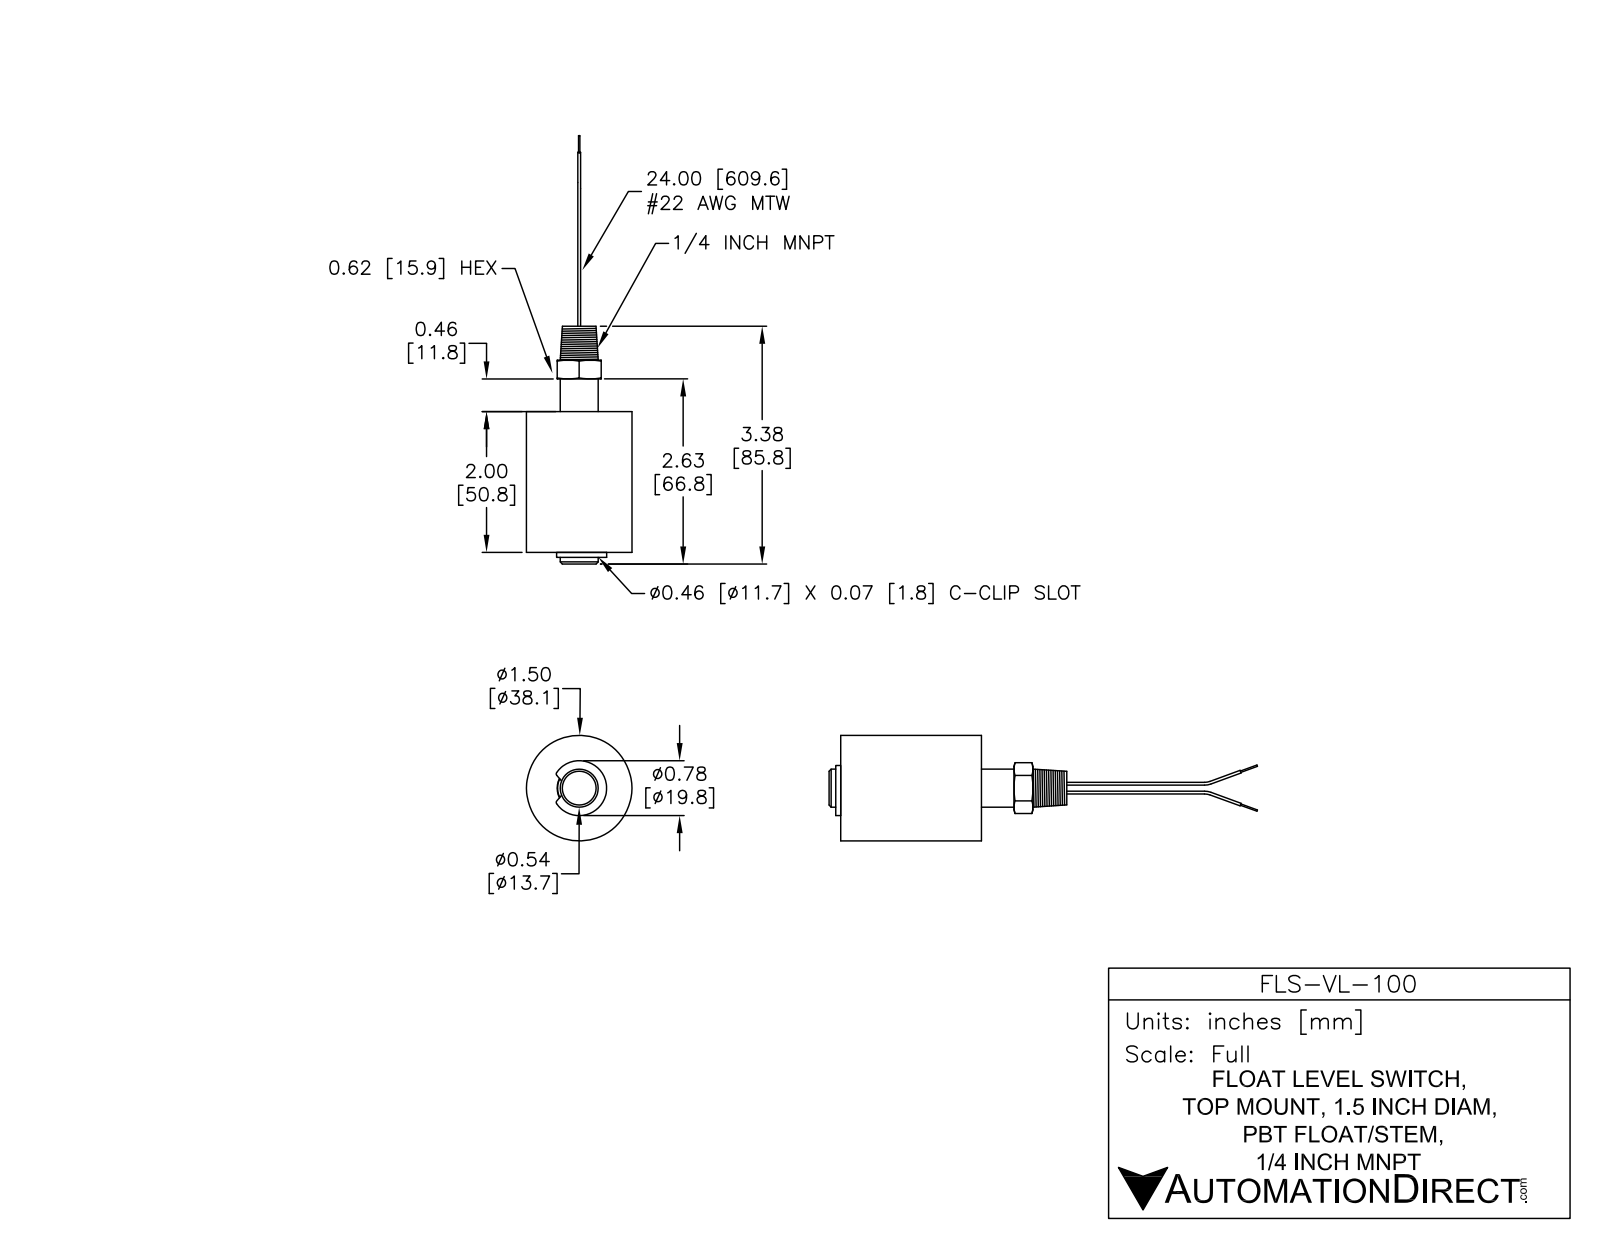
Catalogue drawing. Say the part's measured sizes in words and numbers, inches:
The part is named "FLS-VL-100". Its 3-D file was written by "SolidWorks 2013 (AUTOMOTIVE_DESIGN)". It is 5 solids with 68 faces: 25 planar, 35 cylindrical and 8 other. Overall it measures 6.099 by 1.5 by 1.5 inches. Its volume is 3.173 cubic inches and its surface area 28.35 square inches. Round holes: 1 of diameter 0.45, 1 of diameter 0.46, 1 of diameter 0.63. Round bosses or shafts: 4 of diameter 0.04, 2 of diameter 0.02, 1 of diameter 1.5, 1 of diameter 0.78, 1 of diameter 0.54. Partial cylindrical surfaces (rounded edges, fillets, slot ends): 4 of radius 0.031. The main face-to-face distances are 1.92, 0.168, 2.087, 0.161, 2.081, 0.076, 0.07, 0.091, 2.011, 0.625.
